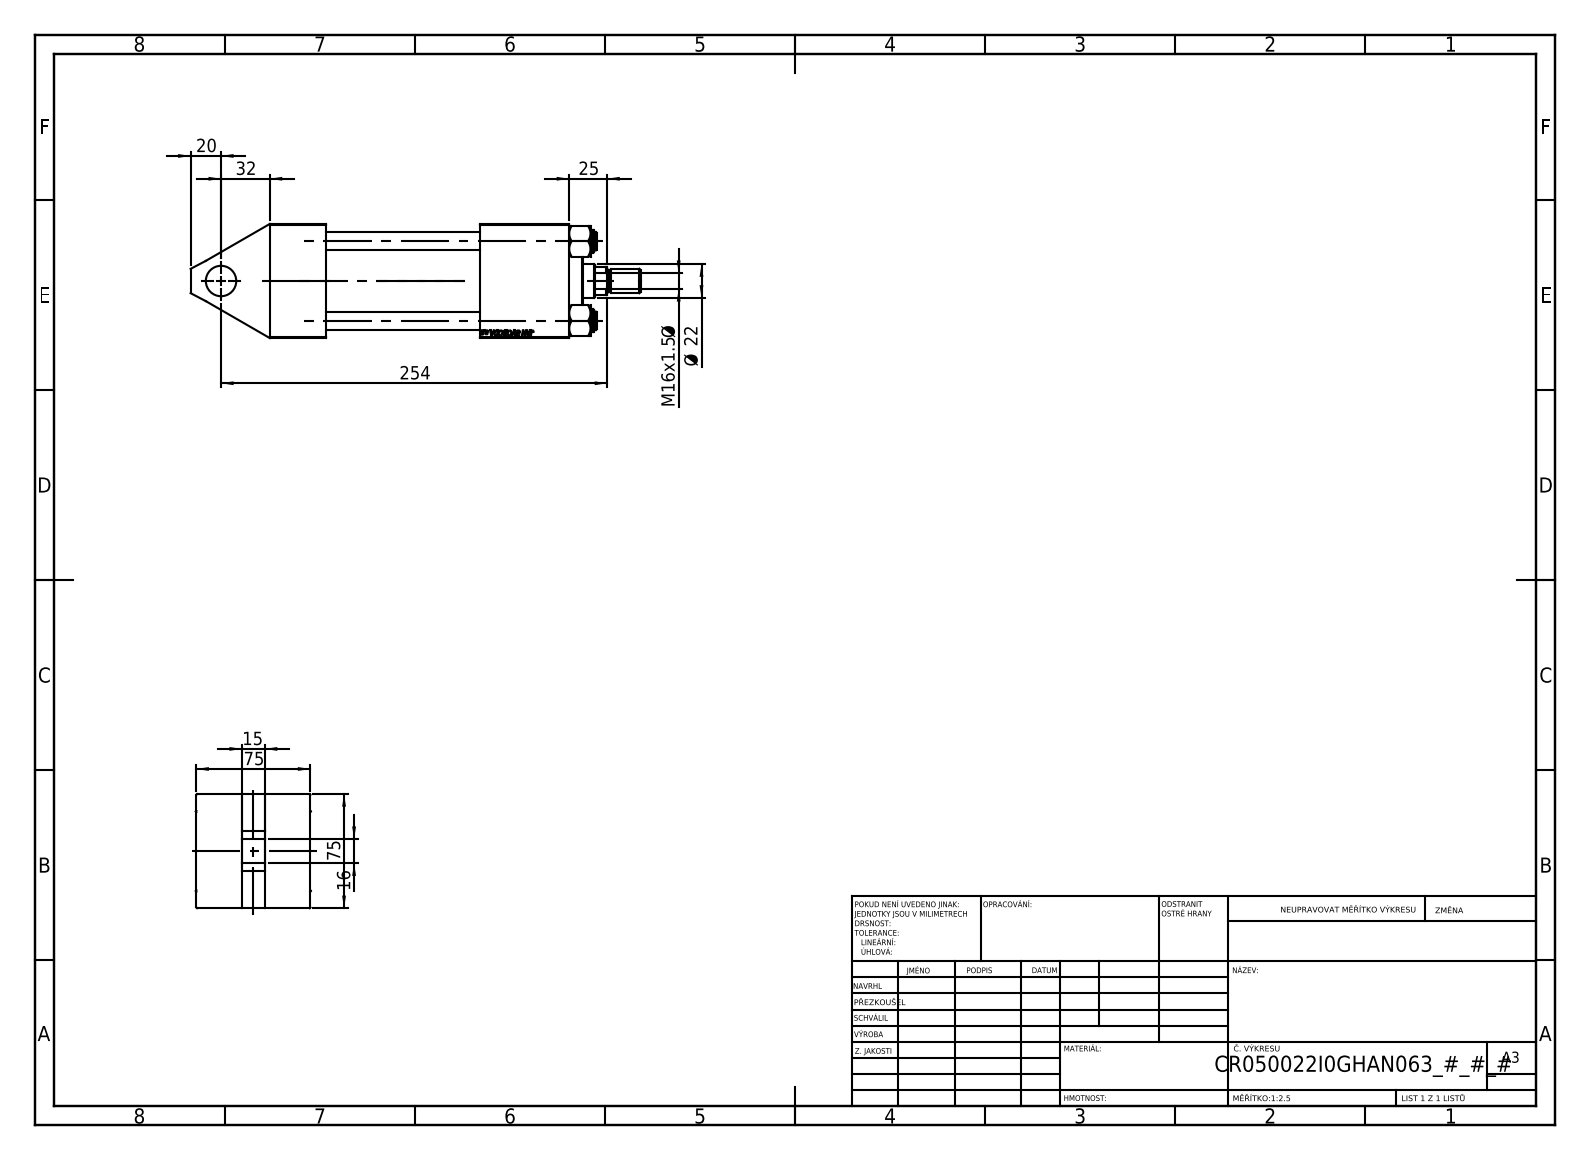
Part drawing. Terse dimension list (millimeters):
name: NUT_M5_I; V215CR_VCP_I; V215CR_I_Body; V215CR_TYCINKA_I (+2 more)
written by: SolidWorks 2019 (CONFIG_CONTROL_DESIGN)
unit: mm
bodies: 12 solids, 1093 faces (506 planar, 85 cylindrical, 502 other)
size: 296 × 75.54 × 75
volume: 761 161 mm³; area: 181 608 mm²
holes: 4× ⌀12, 2× ⌀7, 2× ⌀20.96, 2× ⌀30, 1× ⌀10.5, 1× ⌀20, 1× ⌀22, 1× ⌀25, 1× ⌀41, 1× ⌀50, 1× ⌀53
bosses: 4× ⌀15, 1× ⌀56, 1× ⌀34, 1× ⌀16, 1× ⌀14
rounds: 1× R10.5
face distances: 75, 160, 37, 197, 30, 45, 138, 101, 59, 168.3
hole spacings: 36.98, 52.3, 73.96, 50.5, 136.5, 187
